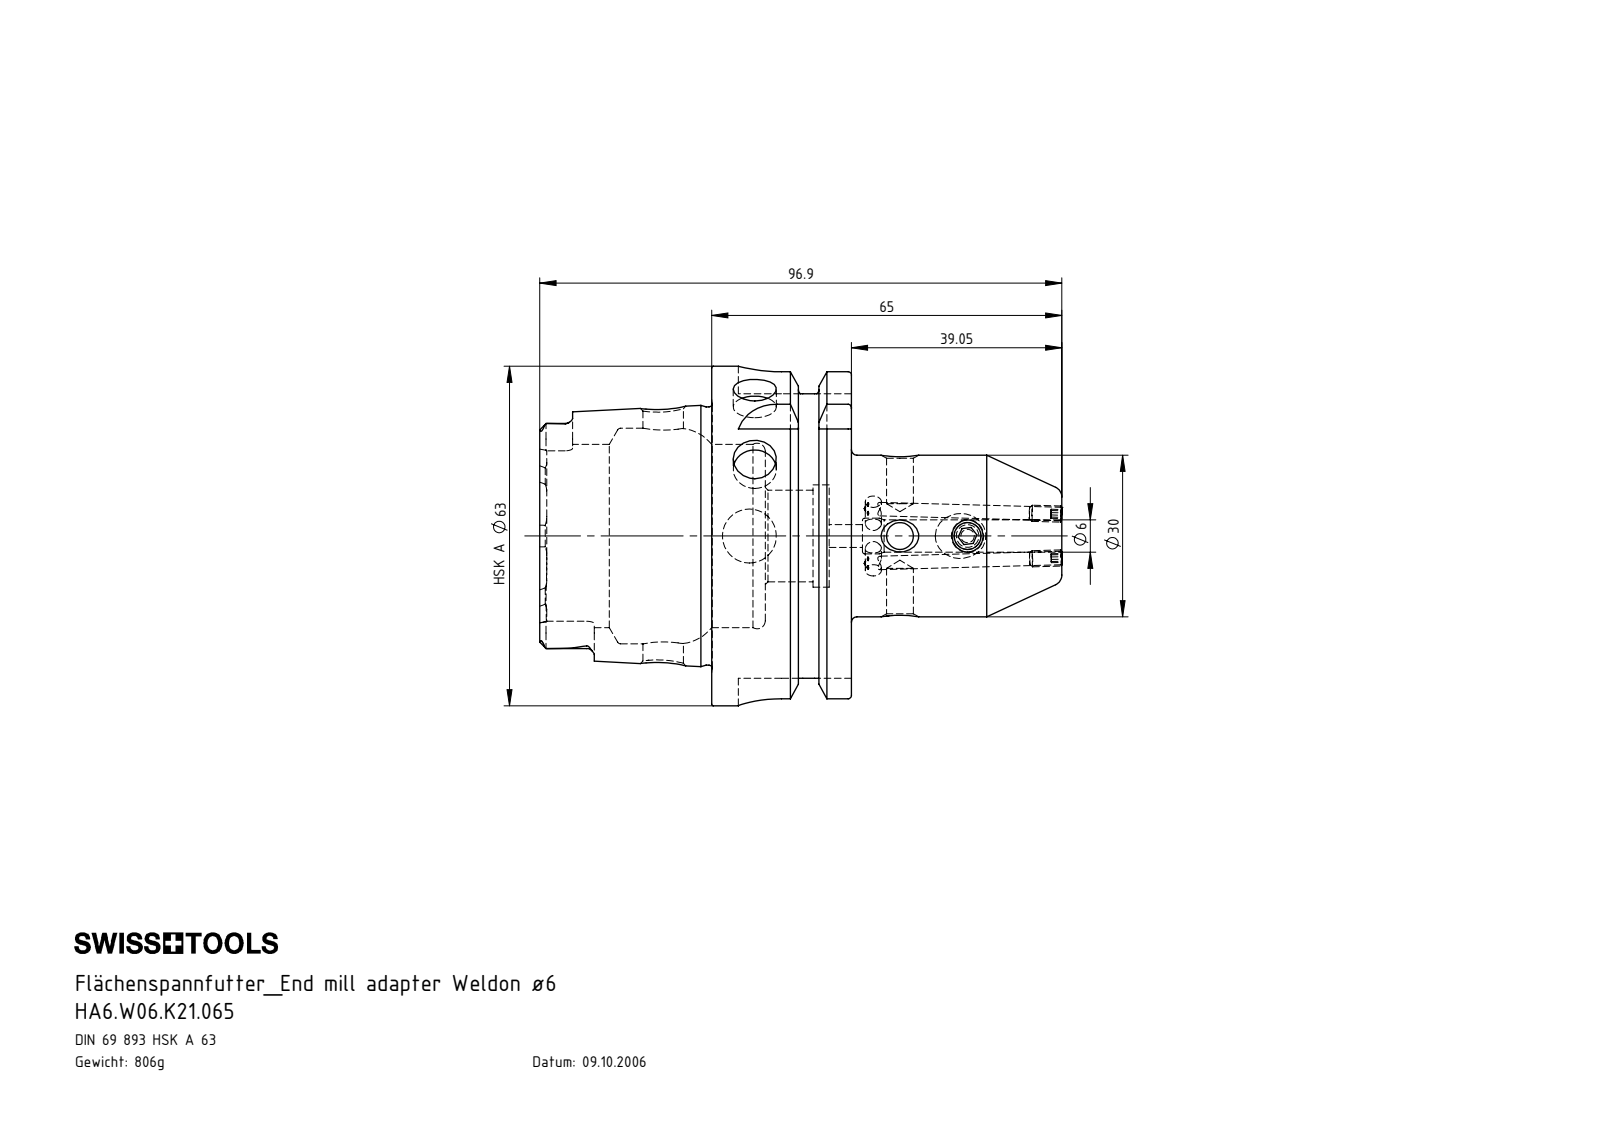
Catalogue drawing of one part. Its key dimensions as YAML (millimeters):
part_name: "HA6.W06.K21.065; ERU-CJ2.001.006; W06-ER1.001.010; HA6-W06.K21.065_C_Fertigbearbeitung"
step_written_by: "SolidWorks 2012 (CONFIG_CONTROL_DESIGN)"
units: millimeters
bodies: {solids: 4, faces: 286, planar: 77, cylindrical: 81, other: 128}
overall_size: [96.98, 63, 63]
volume: 102715
surface_area: 27901
round_holes:
  - {diameter: 5, count: 3}
  - {diameter: 2.5, count: 2}
  - {diameter: 8, count: 2}
  - {diameter: 3, count: 1}
  - {diameter: 4.2, count: 1}
  - {diameter: 6, count: 1}
  - {diameter: 6.6, count: 1}
  - {diameter: 7.5, count: 1}
  - {diameter: 10, count: 1}
  - {diameter: 17, count: 1}
  - {diameter: 19, count: 1}
  - {diameter: 34, count: 1}
round_bosses_or_shafts:
  - {diameter: 3, count: 2}
  - {diameter: 63, count: 1}
  - {diameter: 54.95, count: 1}
  - {diameter: 47.94, count: 1}
  - {diameter: 30, count: 1}
  - {diameter: 6, count: 1}
partial_cylinders:
  - {radius: 1.4, count: 6}
  - {radius: 2.88, count: 4}
  - {radius: 8, count: 4}
face_to_face_distances: [25.95, 16, 9.95, 31.9, 41.85, 57.85, 21.8, 52.8, 11.85, 53.7]
hole_center_spacings: [12.55, 27.95, 40.5, 43.95]
